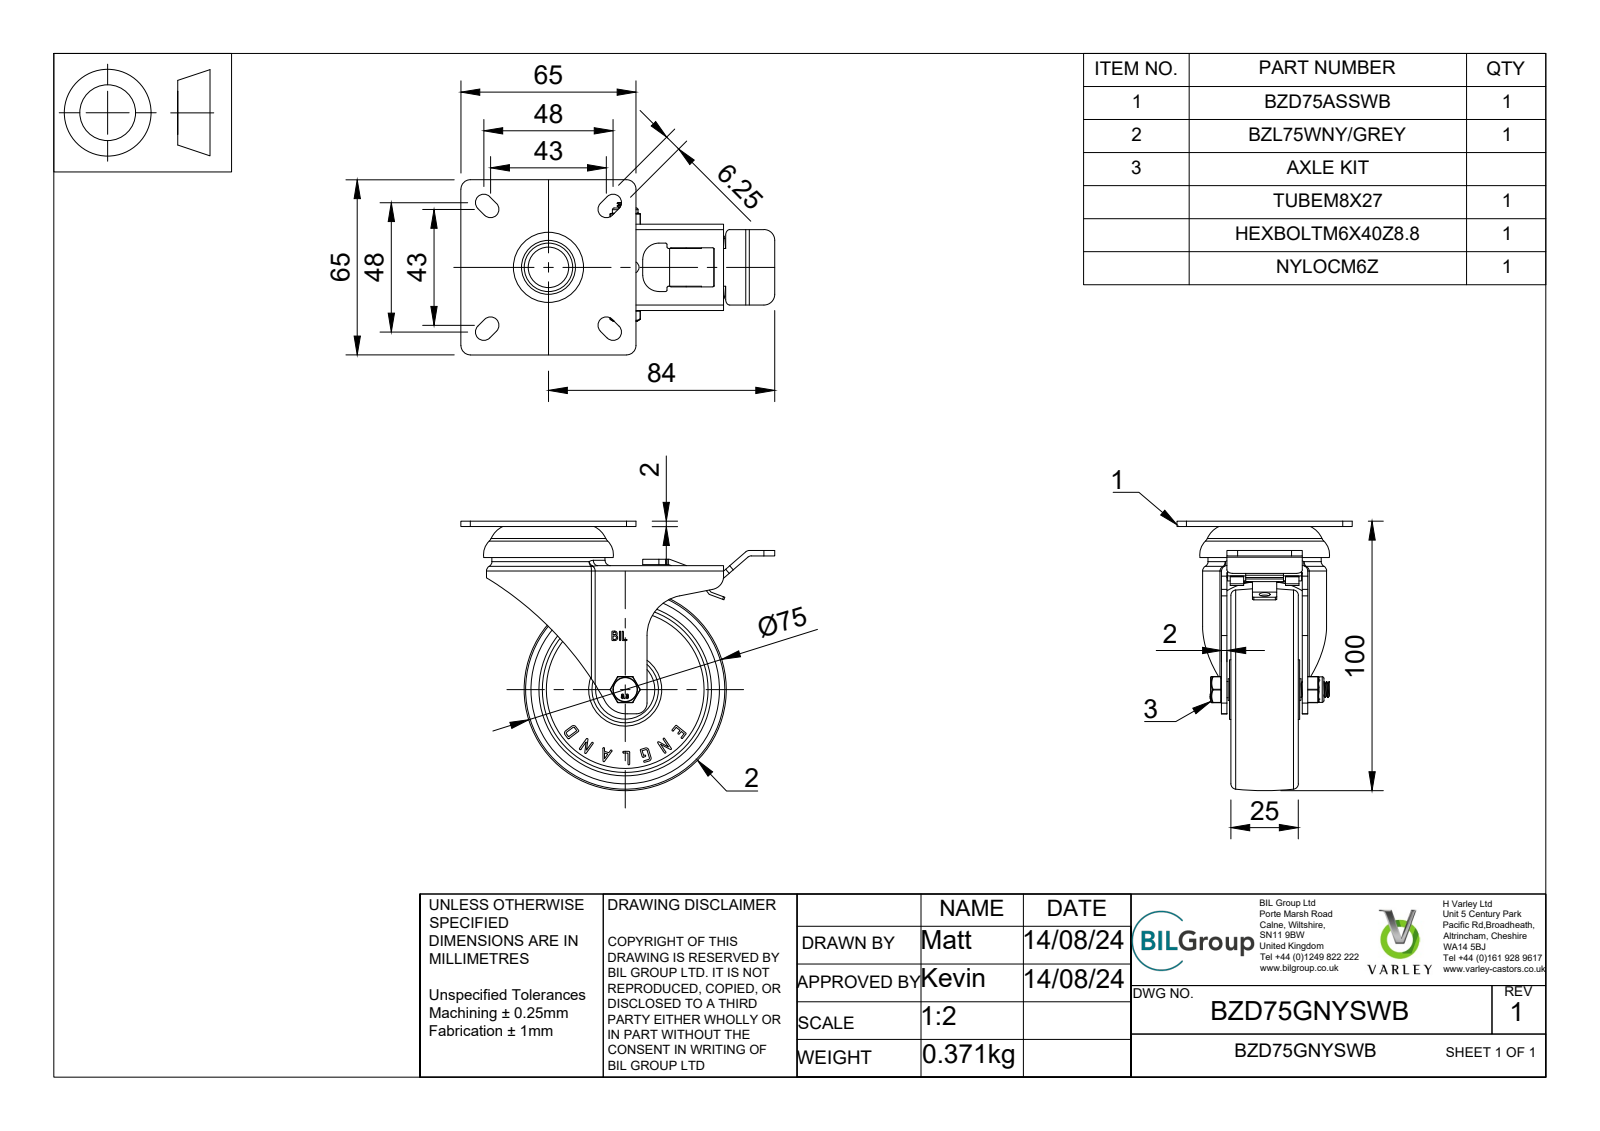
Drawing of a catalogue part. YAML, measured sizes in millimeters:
part_name: "BZD75GNYSWB v3; BZD75ASSWB v1; ZINC PLATED, PRESSED STEEL TOP PLATE; ZINC PLATED, PRESSED STEEL TOP PLATE Geometry (+8 more)"
step_written_by: "Autodesk Translation Framework v13.14.0.145 (AUTOMOTIVE_DESIGN)"
units: millimeters
bodies: {solids: 29, faces: 911, planar: 414, cylindrical: 271, other: 226}
overall_size: [116.5, 100, 65]
volume: 95330
surface_area: 58565
round_holes:
  - {diameter: 4, count: 1}
  - {diameter: 4.5, count: 1}
  - {diameter: 6, count: 1}
  - {diameter: 6.2, count: 1}
  - {diameter: 7, count: 1}
  - {diameter: 8.2, count: 1}
  - {diameter: 20, count: 1}
  - {diameter: 38, count: 1}
  - {diameter: 42, count: 1}
  - {diameter: 45.14, count: 1}
  - {diameter: 61.5, count: 1}
round_bosses_or_shafts:
  - {diameter: 37, count: 1}
  - {diameter: 18, count: 1}
  - {diameter: 17, count: 1}
  - {diameter: 10, count: 1}
  - {diameter: 9.5, count: 1}
  - {diameter: 8.5, count: 1}
  - {diameter: 8, count: 1}
  - {diameter: 5.88, count: 1}
partial_cylinders:
  - {radius: 0.75, count: 90}
  - {radius: 0.5, count: 17}
  - {radius: 0.25, count: 14}
  - {radius: 1.5, count: 12}
  - {radius: 2, count: 11}
  - {radius: 3.12, count: 8}
  - {radius: 1, count: 7}
  - {radius: 0.23, count: 4}
face_to_face_distances: [2, 11, 13, 17, 6, 19, 30, 16.5, 14.5, 9.5]
hole_center_spacings: [31.37]
